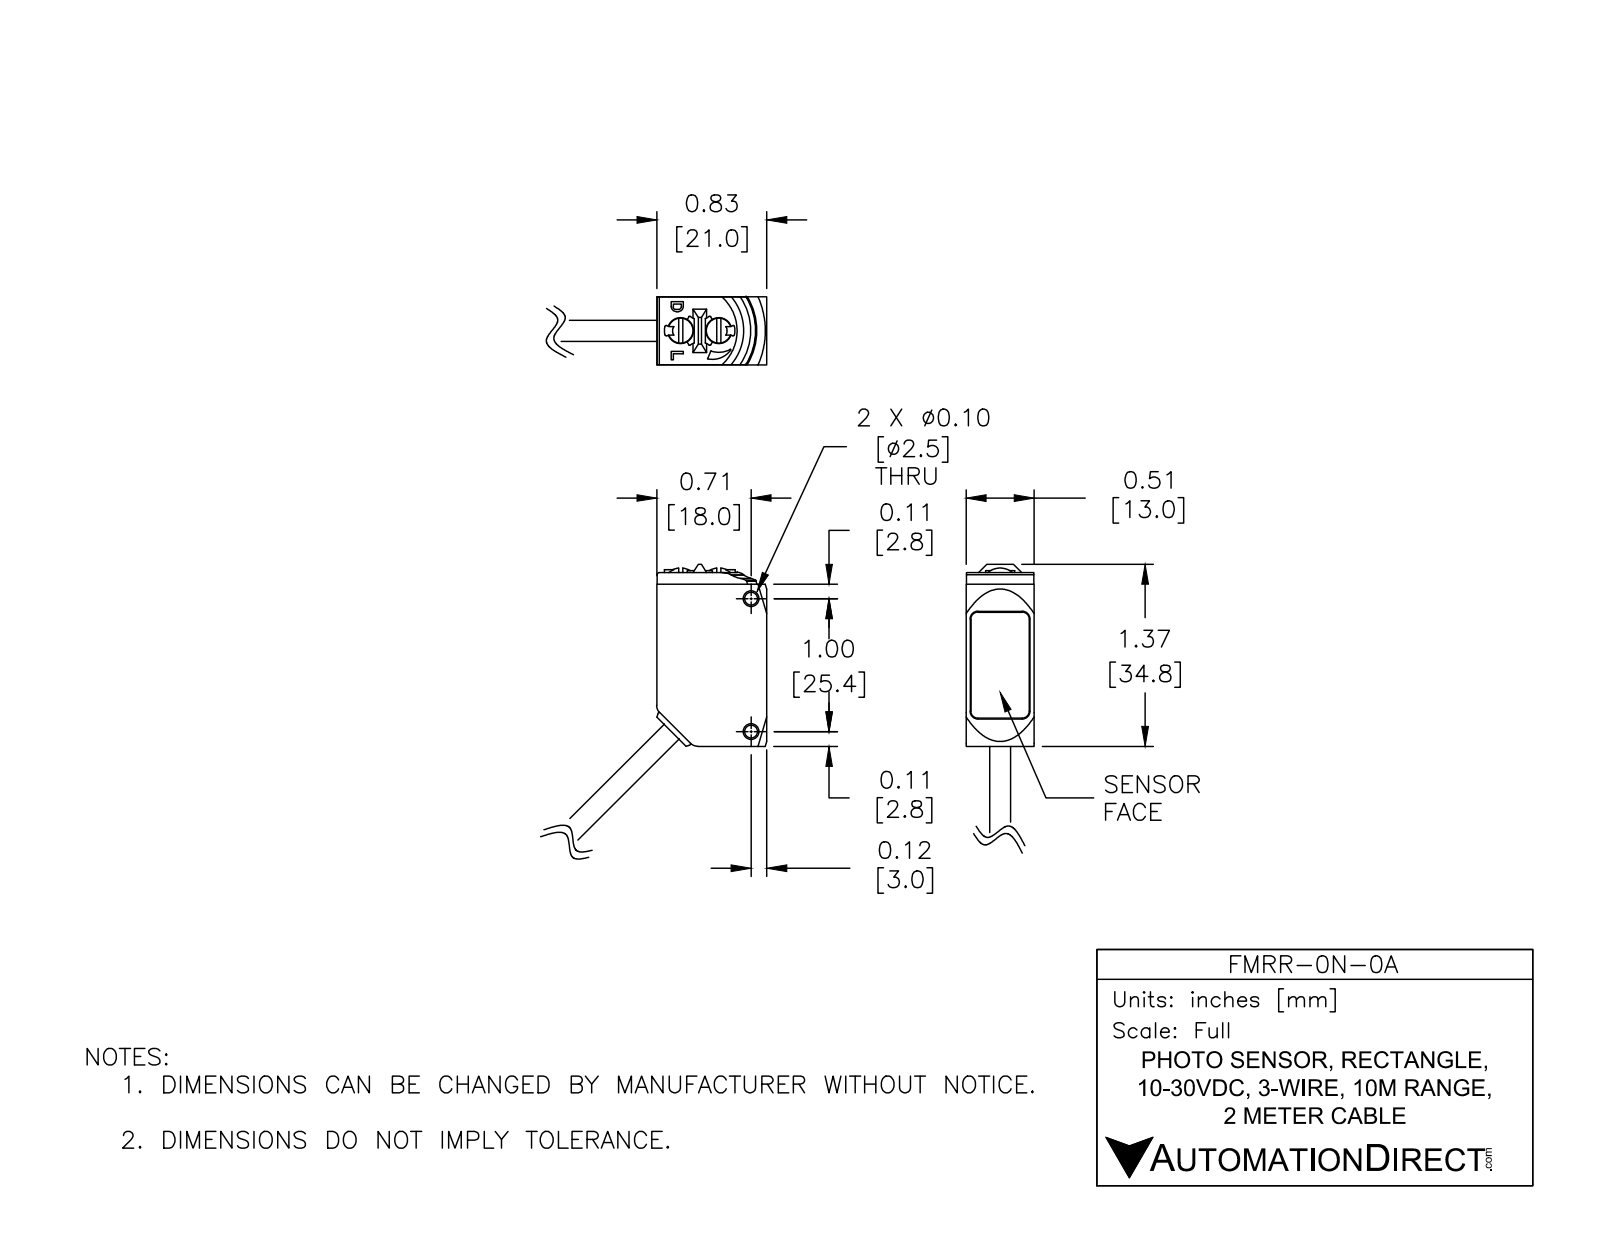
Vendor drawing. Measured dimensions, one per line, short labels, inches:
name: FMRR-0N-0A
written by: SolidWorks 2017 (AUTOMOTIVE_DESIGN)
unit: in
bodies: 1 solid, 186 faces (89 planar, 72 cylindrical, 25 other)
size: 2.084 × 1.541 × 0.512
volume: 0.542 in³; area: 5.476 in²
holes: 2× ⌀0.097, 2× ⌀0.197
bosses: 2× ⌀0.189, 1× ⌀0.157
rounds: 7× R0.018, 7× R0.02, 4× R0.008, 4× R0.01, 4× R0.051, 4× R0.059, 3× R0.004, 2× R0.018
face distances: 0.512, 0.827, 1.307, 0.035, 0.51, 0.031, 0.48, 0.037, 0.474, 0.472
hole spacings: 0.287, 1
